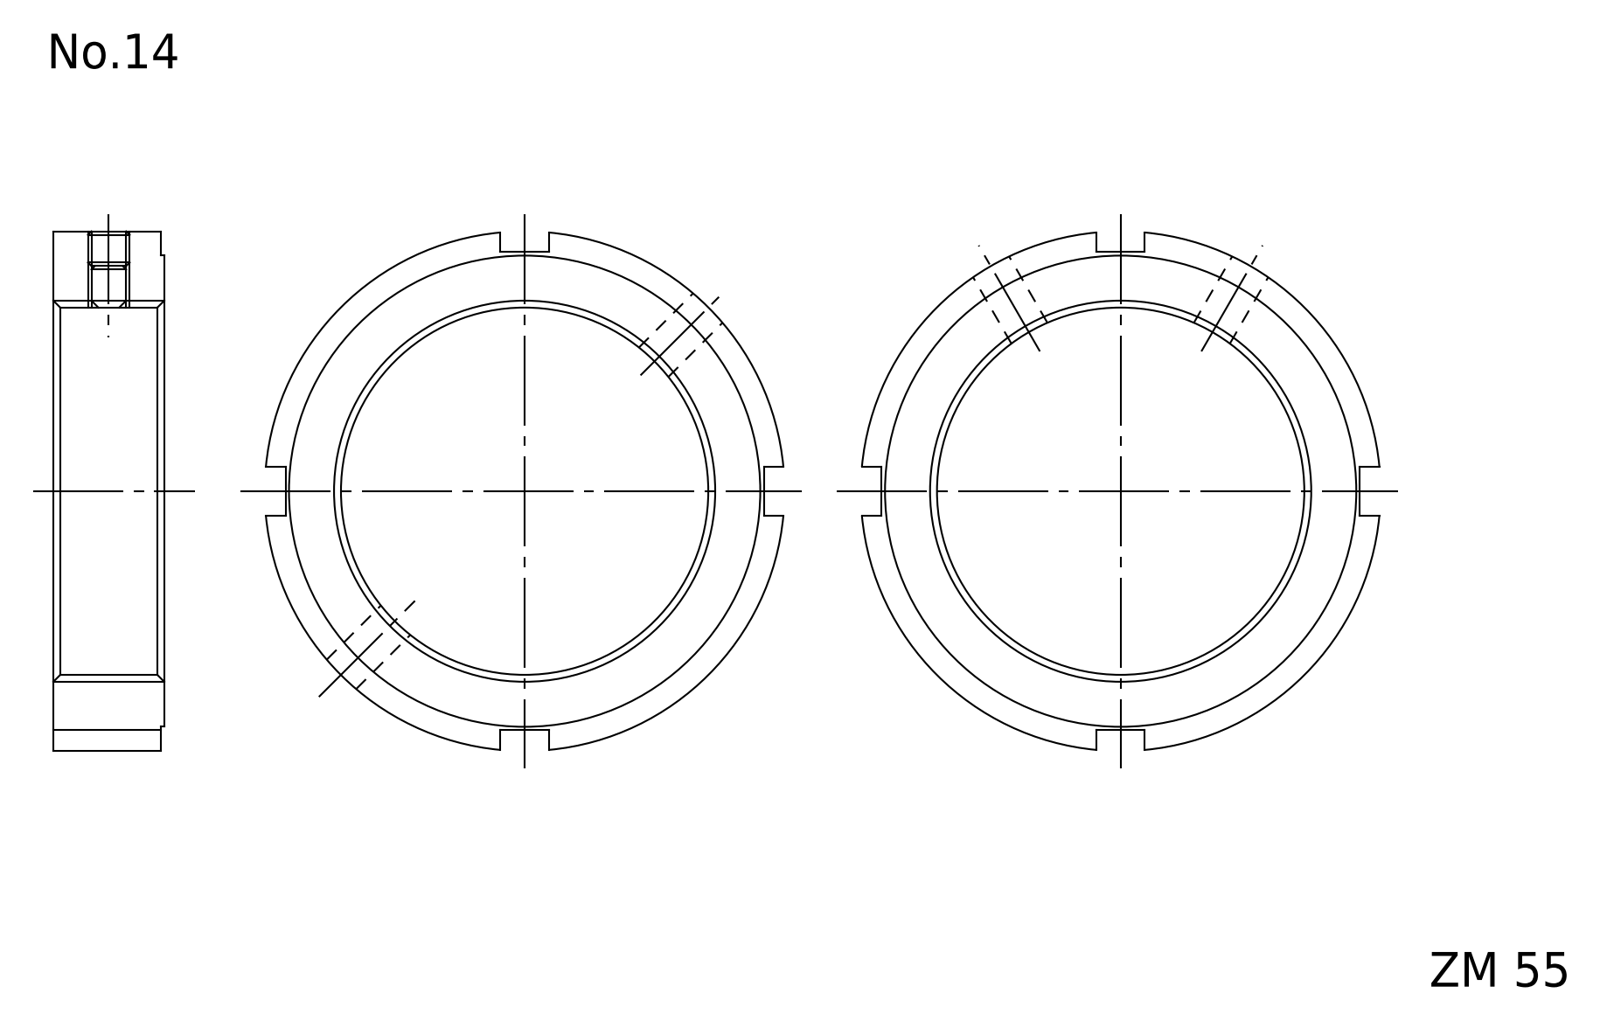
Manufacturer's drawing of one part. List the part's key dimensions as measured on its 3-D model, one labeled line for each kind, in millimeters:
Part name (STEP PRODUCT): FKD ZM 55
STEP written by: Autodesk Inventor 2011 (AUTOMOTIVE_DESIGN)
Units: millimetres
Bodies: 1 solid, 23 faces (15 planar, 8 cylindrical, 0 other)
Overall size (bounding box): 74.67 × 74.67 × 16
Volume: 30 621 mm³ · Surface area: 11 027 mm²
Round holes (diameter × count): ⌀4.92 ×2, ⌀55 ×1
Round bosses / shafts (diameter × count): ⌀75 ×1, ⌀68 ×1
Main face-to-face distances: 16, 0.5, 15.5, 31, 38, 69, 7
